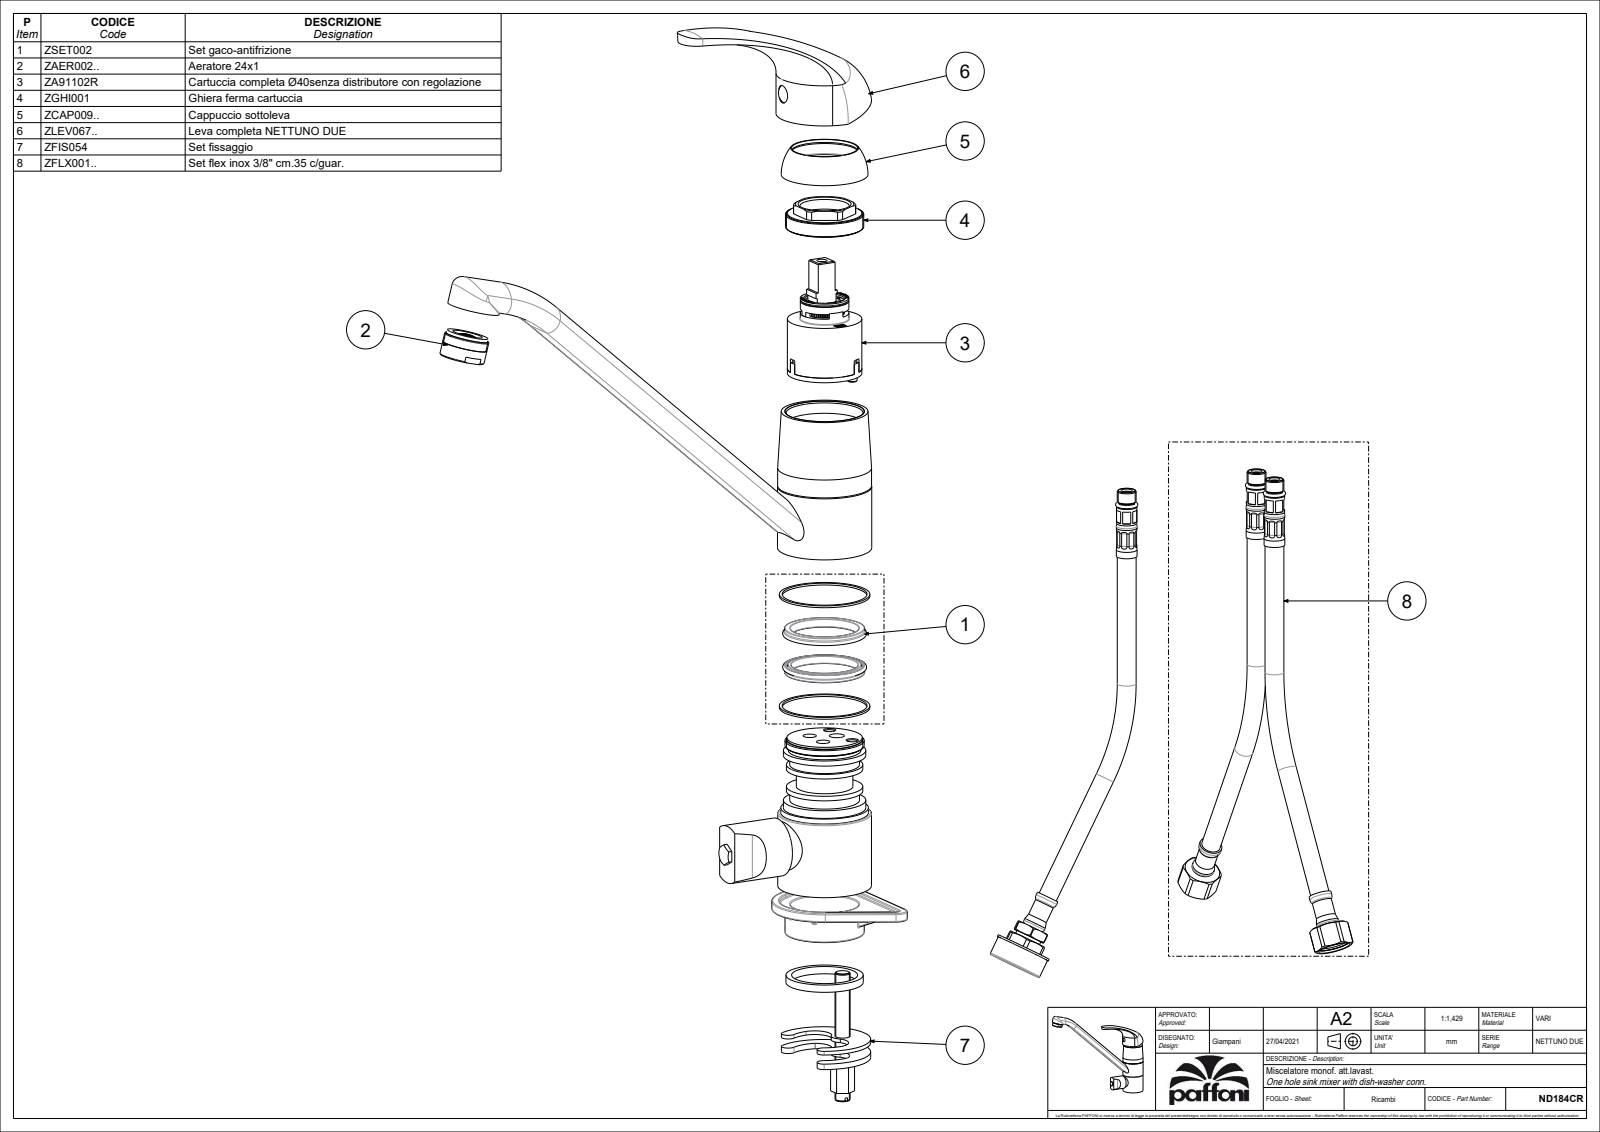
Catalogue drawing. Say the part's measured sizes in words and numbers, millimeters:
The part is named "ND184CR". Its 3-D file was written by "CREO PARAMETRIC BY PTC INC, 2020044 (CONFIG_CONTROL_DESIGN)". It is 1 solid with 228 faces: 69 planar, 79 cylindrical and 80 other. Overall it measures 253.52 by 218.37 by 51 millimeters. Its volume is 382 581 cubic millimeters and its surface area 67 337 square millimeters. Round holes: 3 of diameter 7, 3 of diameter 9, 2 of diameter 6, 2 of diameter 11.2, 1 of diameter 6.8, 1 of diameter 8.5, 1 of diameter 9.2, 1 of diameter 18.6, 1 of diameter 21.5, 1 of diameter 22, 1 of diameter 24, 1 of diameter 43. Round bosses or shafts: 1 of diameter 50, 1 of diameter 49.8, 1 of diameter 49.7, 1 of diameter 46.5, 1 of diameter 44.8, 1 of diameter 43.7, 1 of diameter 33, 1 of diameter 31. Partial cylindrical surfaces (rounded edges, fillets, slot ends): 4 of radius 5.5, 2 of radius 7, 2 of radius 16.5, 1 of radius 3.9, 1 of radius 4, 1 of radius 65. The main face-to-face distances are 129.7, 0.9, 128.8, 73.9, 73, 55.8, 31, 40.4, 39.5, 33.5. The hole center spacings are 9.5, 13.79, 14.53, 10, 11, 14.2, 19, 21.
